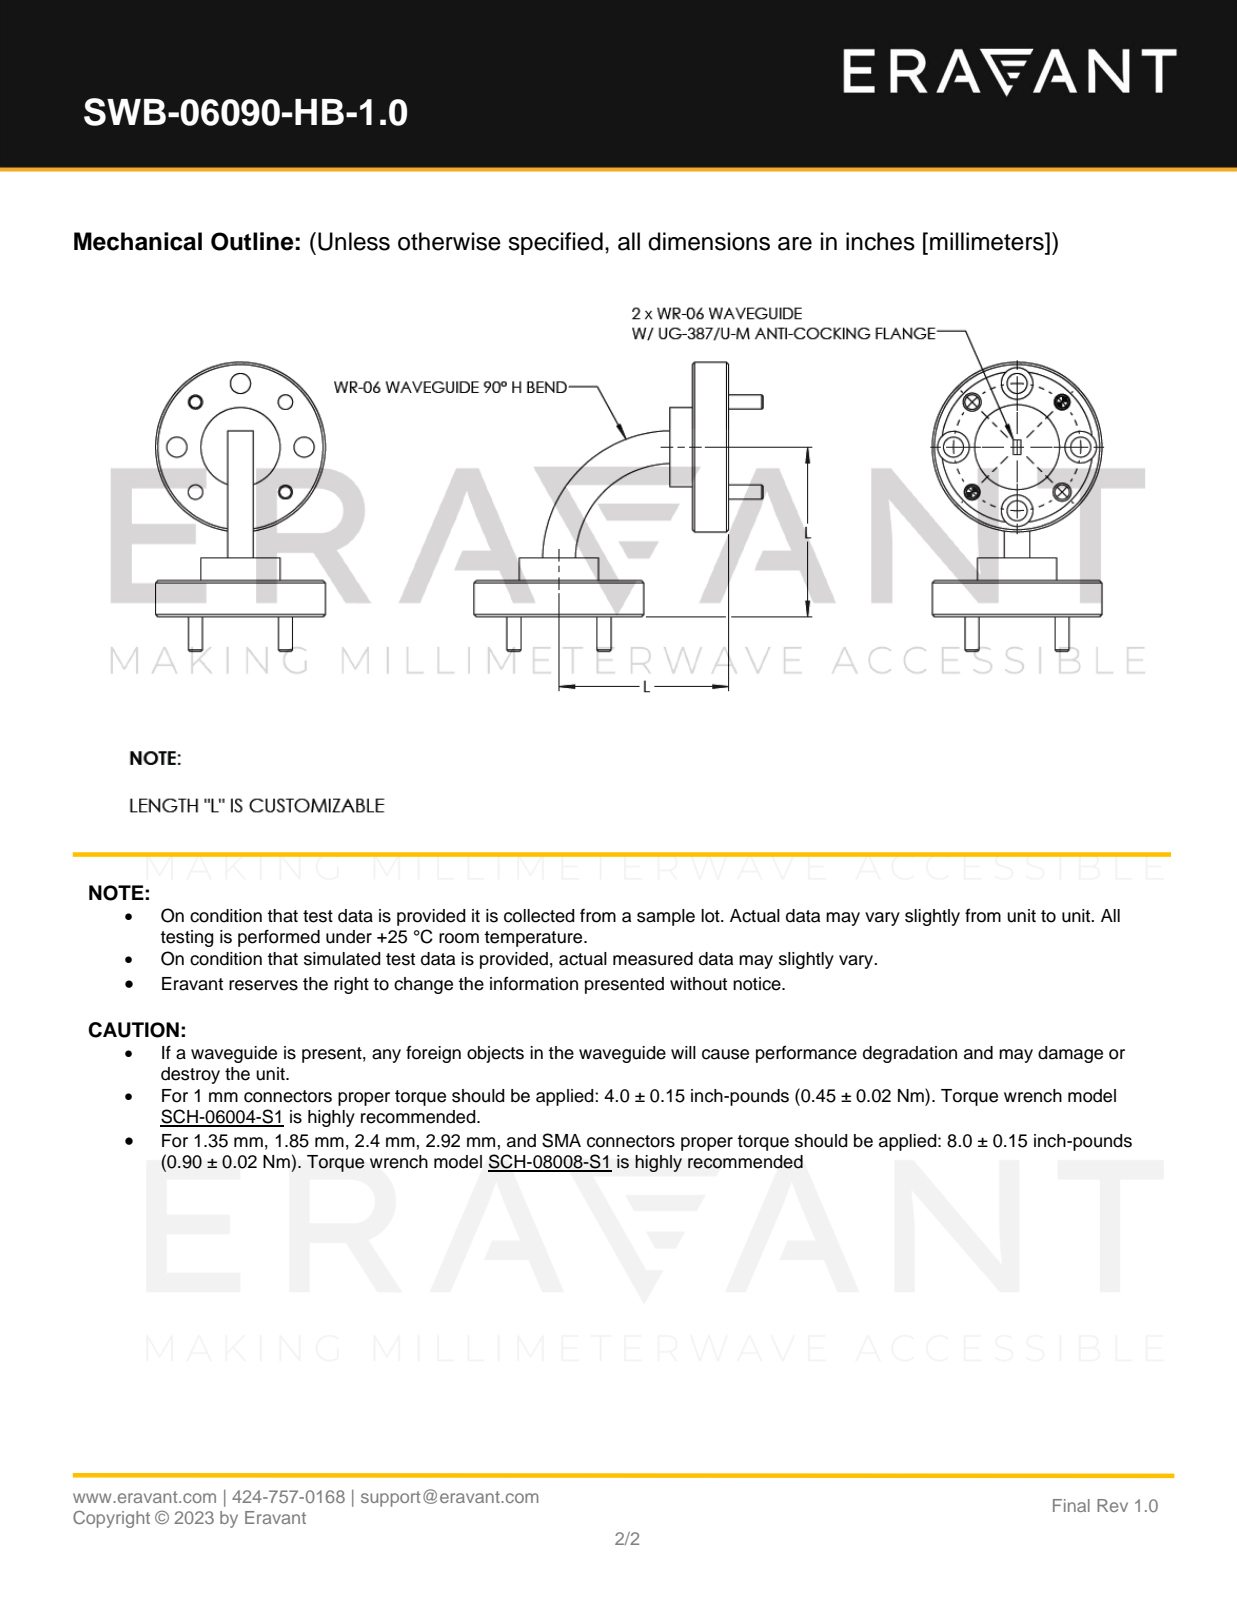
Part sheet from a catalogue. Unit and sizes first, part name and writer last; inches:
Units: inches
Overall size (bounding box): 1.528 × 1.527 × 0.75
Round holes (diameter × count): ⌀0.089 ×8, ⌀0.14 ×8, ⌀0.061 ×4, ⌀0.064 ×4, ⌀0.67 ×2
Round bosses / shafts (diameter × count): ⌀0.063 ×4, ⌀0.75 ×2, ⌀0.375 ×2, ⌀0.35 ×2
Partial cylindrical surfaces — rounded edges, fillets, slot ends (radius × count): R0.428 ×1, R0.573 ×1
Main face-to-face distances: 0.16, 0.03, 0.13, 0.113, 0.26, 0.23, 0.1, 0.02, 0.05, 0.11
Hole centre spacings: 0.215, 0.281, 0.398, 0.519, 0.562
Volume: 0.159 in³ · Surface area: 4.139 in²
Bodies: 5 solids, 160 faces (42 planar, 78 cylindrical, 40 other)
Part name (STEP PRODUCT): WB-HD-A-L, 1 inch
STEP written by: SolidWorks 2021 (AUTOMOTIVE_DESIGN)
